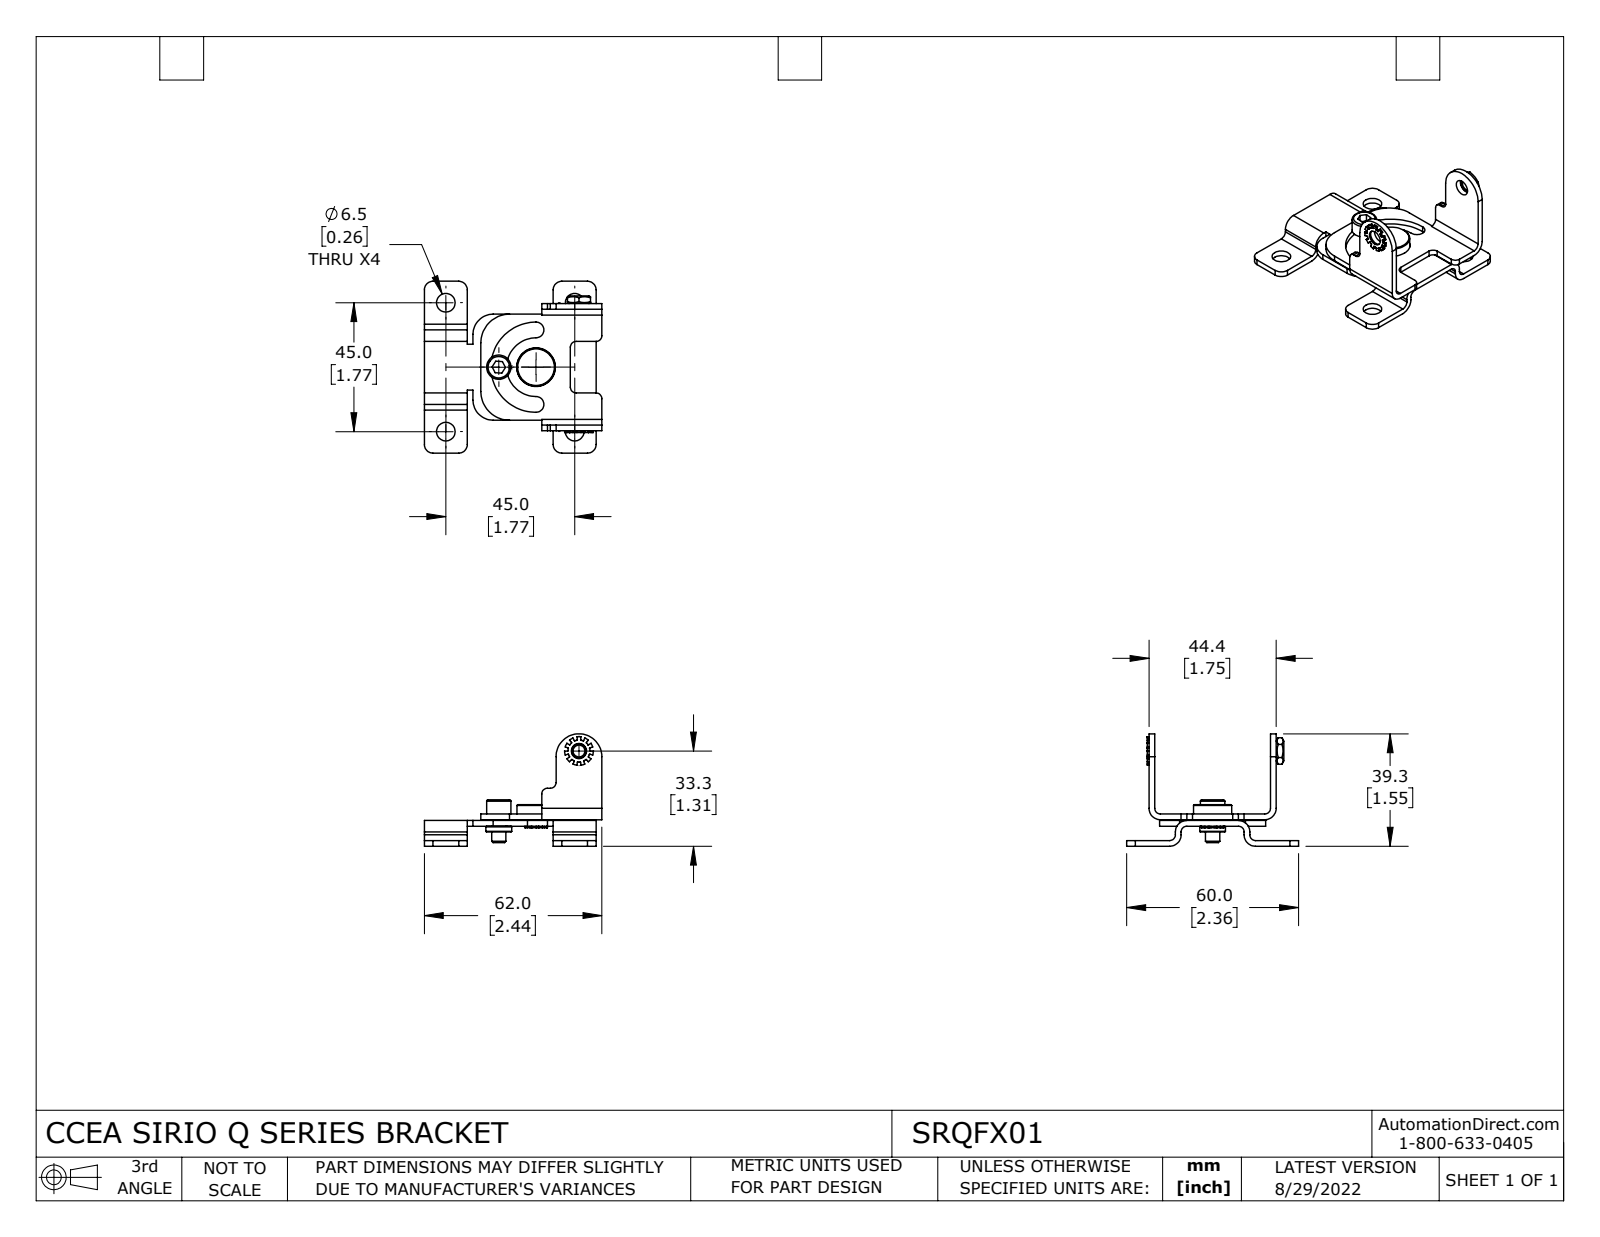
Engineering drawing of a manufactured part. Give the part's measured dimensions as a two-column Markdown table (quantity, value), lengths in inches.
| quantity | value |
| --- | --- |
| part name | SRQFX01 |
| STEP written by | SolidWorks 2021 (CONFIG_CONTROL_DESIGN) |
| units | inches |
| bodies | 8 solids, 337 faces (129 planar, 182 cylindrical, 26 other) |
| overall size | 2.441 × 2.362 × 1.545 |
| volume | 0.669 in³ |
| surface area | 20.1 in² |
| round holes (diameter × count) | 0.256 × 4, 0.163 × 2, 0.169 × 2, 0.128 × 1, 0.197 × 1, 0.209 × 1, 0.217 × 1, 0.531 × 1 |
| round bosses / shafts (diameter × count) | 0.524 × 1, 0.354 × 1, 0.335 × 1, 0.197 × 1 |
| partial cylindrical surfaces (radius × count) | 0.005 × 22, 0.006 × 22, 0.079 × 12, 0.118 × 8, 0.157 × 7, 0.276 × 4, 0.108 × 2, 0.394 × 2 |
| main face-to-face distances | 0.079, 0.089, 0.276, 0.364, 0.167, 0.197, 1.669, 0.354, 0.285, 0.443 |
| hole center spacings | 1.772, 1.033, 1.147, 1.369, 1.524, 2.506, 0.512 |
